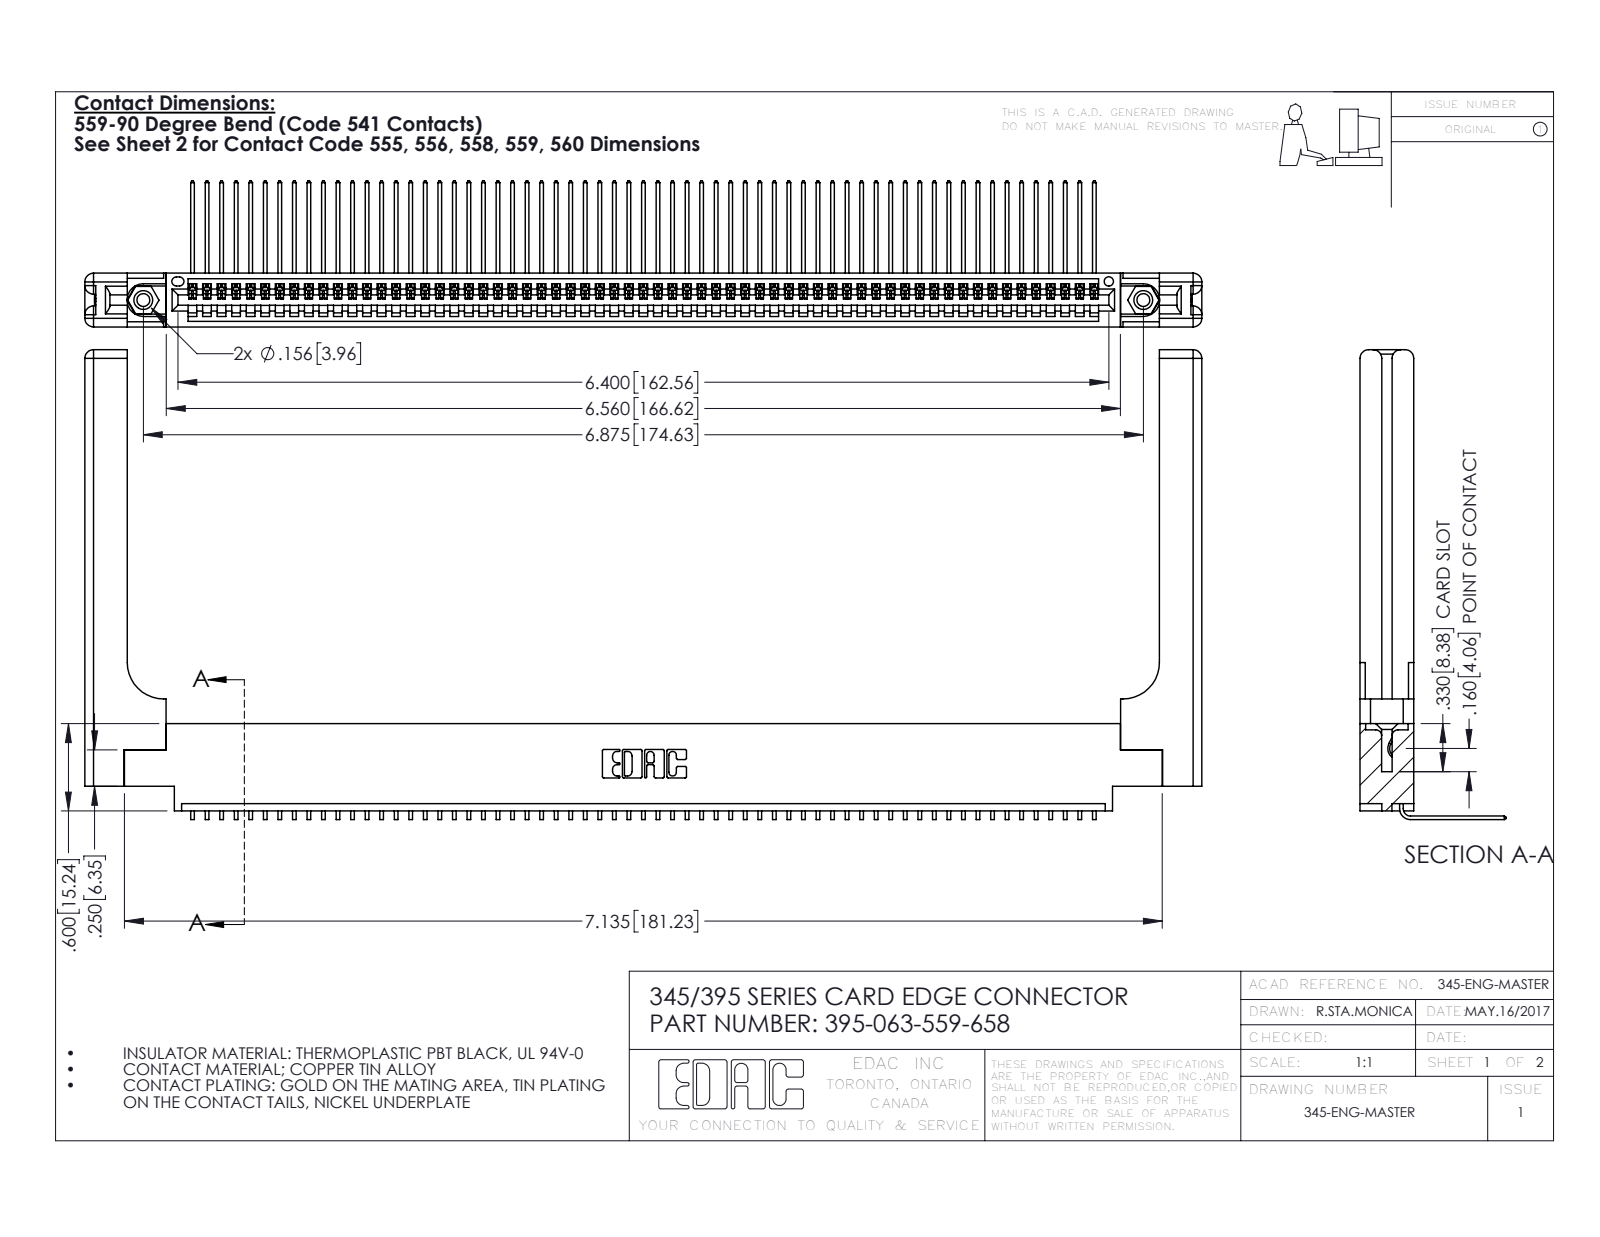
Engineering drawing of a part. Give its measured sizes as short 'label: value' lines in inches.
name: 345-220-058_345-220-058; 345-250-001_345-250-001-102; 395-063-559-658; 345-292-001_558 559 Tail - 1 (+1 more)
written by: SolidWorks 2016 (CONFIG_CONTROL_DESIGN)
unit: in
bodies: 68 solids, 4166 faces (2878 planar, 1228 cylindrical, 60 other)
size: 7.679 × 3.229 × 1.005
volume: 1.666 in³; area: 49.49 in²
holes: 2× ⌀0.089, 2× ⌀0.125, 2× ⌀0.156, 1× ⌀0.064
bosses: 2× ⌀0.155
rounds: 126× R0.006, 22× R0.01, 16× R0.06, 6× R0.007, 6× R0.031, 3× R0.026, 2× R0.03, 2× R0.031
face distances: 0.37, 0.072, 0.298, 0.098, 0.272, 0.025, 0.2, 0.225, 0.148, 0.15
hole spacings: 0.27, 6.639, 6.875
